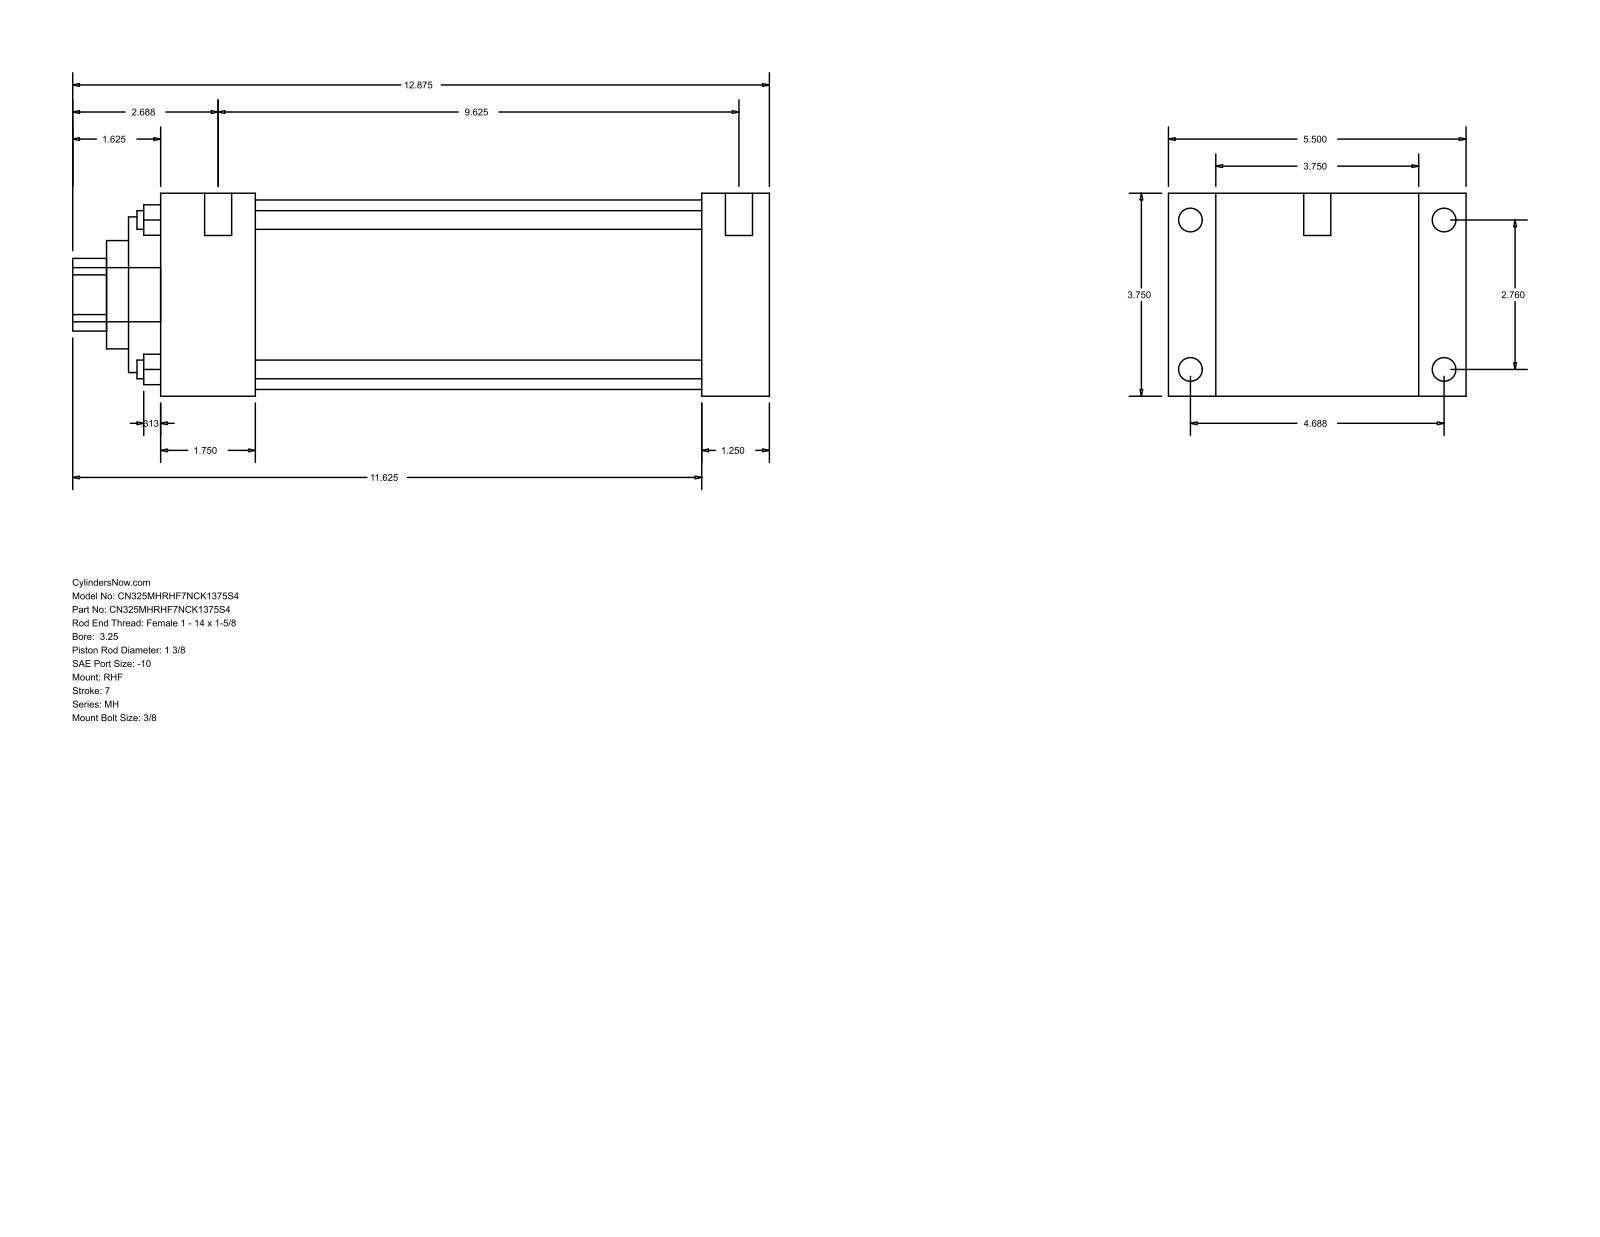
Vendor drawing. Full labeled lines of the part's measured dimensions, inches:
Part name (STEP PRODUCT): MH_RHF__0325_1.375
STEP written by: GSSL Pune (CONFIG_CONTROL_DESIGN)
Units: inches
Bodies: 0 solids, 90 faces (61 planar, 29 cylindrical, 0 other)
Overall size (bounding box): 12.875 × 5.5 × 3.75
Round holes (diameter × count): ⌀0.345 ×4, ⌀1.375 ×1, ⌀2 ×1, ⌀2.875 ×1, ⌀3.5 ×1
Round bosses / shafts (diameter × count): ⌀0.438 ×4, ⌀0.219 ×4, ⌀0.5 ×2, ⌀1 ×1
Partial cylindrical surfaces — rounded edges, fillets, slot ends (radius × count): R0.672 ×1
Main face-to-face distances: 3.75, 1.25, 0.875, 4.625, 10, 11.25, 5.5, 1.75, 8.25, 9.5
Hole centre spacings: 1.952, 2.76, 3.903
